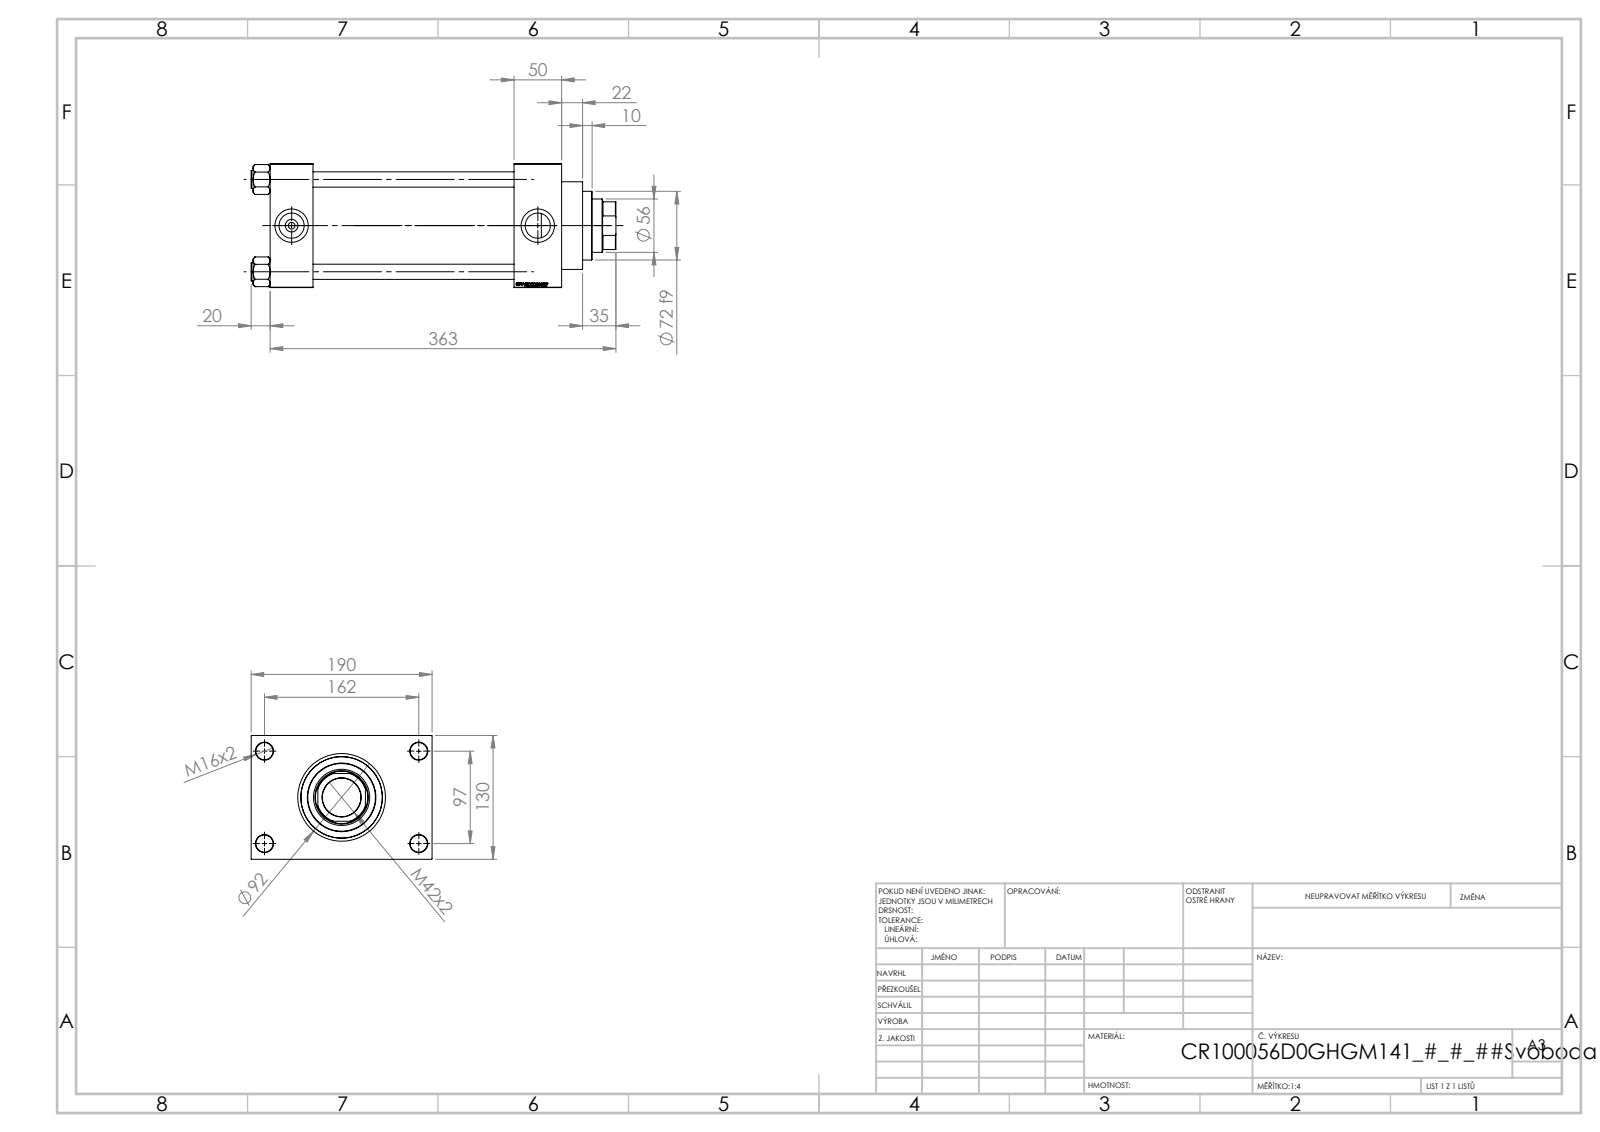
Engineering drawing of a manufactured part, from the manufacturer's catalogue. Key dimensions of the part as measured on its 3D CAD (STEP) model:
Part name (STEP PRODUCT): V215CR_D_TYCINKA; NUT_M5_D; V215CR_D_Body; V215_VC_A (+1 more)
STEP written by: SolidWorks 2019 (CONFIG_CONTROL_DESIGN)
Units: millimetres
Bodies: 11 solids, 1151 faces (545 planar, 88 cylindrical, 518 other)
Overall size (bounding box): 383 × 190 × 130
Volume: 3 221 000 mm³ · Surface area: 505 745 mm²
Round holes (diameter × count): ⌀16 ×4, ⌀18 ×4, ⌀7 ×2, ⌀26.44 ×2, ⌀35 ×2, ⌀40.5 ×1, ⌀56 ×1, ⌀59 ×1, ⌀76 ×1, ⌀85.5 ×1, ⌀100 ×1
Round bosses / shafts (diameter × count): ⌀19 ×4, ⌀106 ×1, ⌀92 ×1, ⌀72 ×1
Partial cylindrical surfaces — rounded edges, fillets, slot ends (radius × count): R27 ×1
Main face-to-face distances: 130, 50, 45, 256, 211, 306, 261, 160, 30, 190
Hole centre spacings: 32.55, 68.52, 94.41, 96.9, 102.27, 129.45, 161.73, 97
